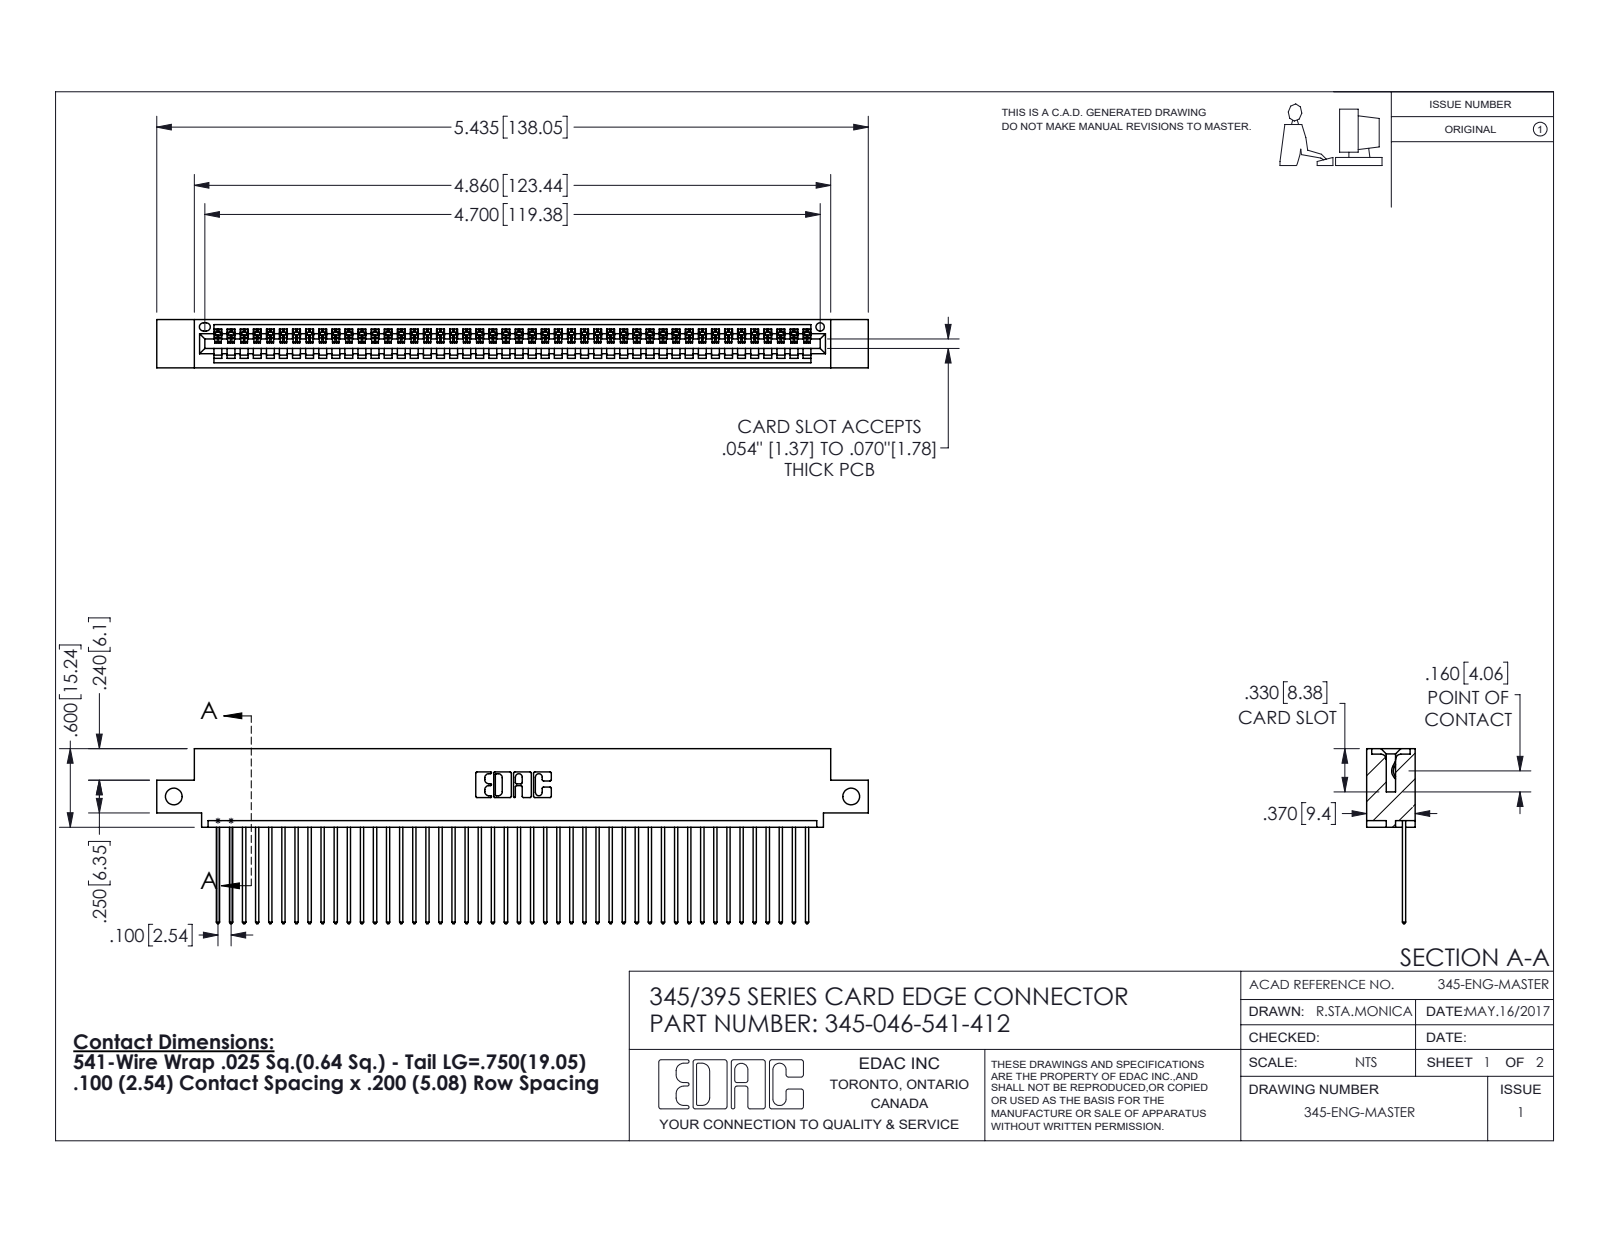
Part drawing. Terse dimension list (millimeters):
name: 345-046-541-412; 345-292-001_345-293-141; 345 Part_0.110 Offset - Side Mount
written by: SolidWorks 2016 (CONFIG_CONTROL_DESIGN)
unit: mm
bodies: 47 solids, 2798 faces (1924 planar, 874 cylindrical, 0 other)
size: 138 × 34 × 9.4
volume: 13 100 mm³; area: 18 340 mm²
holes: 2× ⌀3.3, 1× ⌀1.6
rounds: 92× R0.2, 92× R0.3, 22× R0.3, 6× R0.2, 6× R0.8, 3× R0.7, 2× R0.8, 2× R1
face distances: 1.8, 7.6, 2.5, 6.9, 0.6, 9.4, 5.1, 5.7, 3.8, 1.8
hole spacings: 131.4
